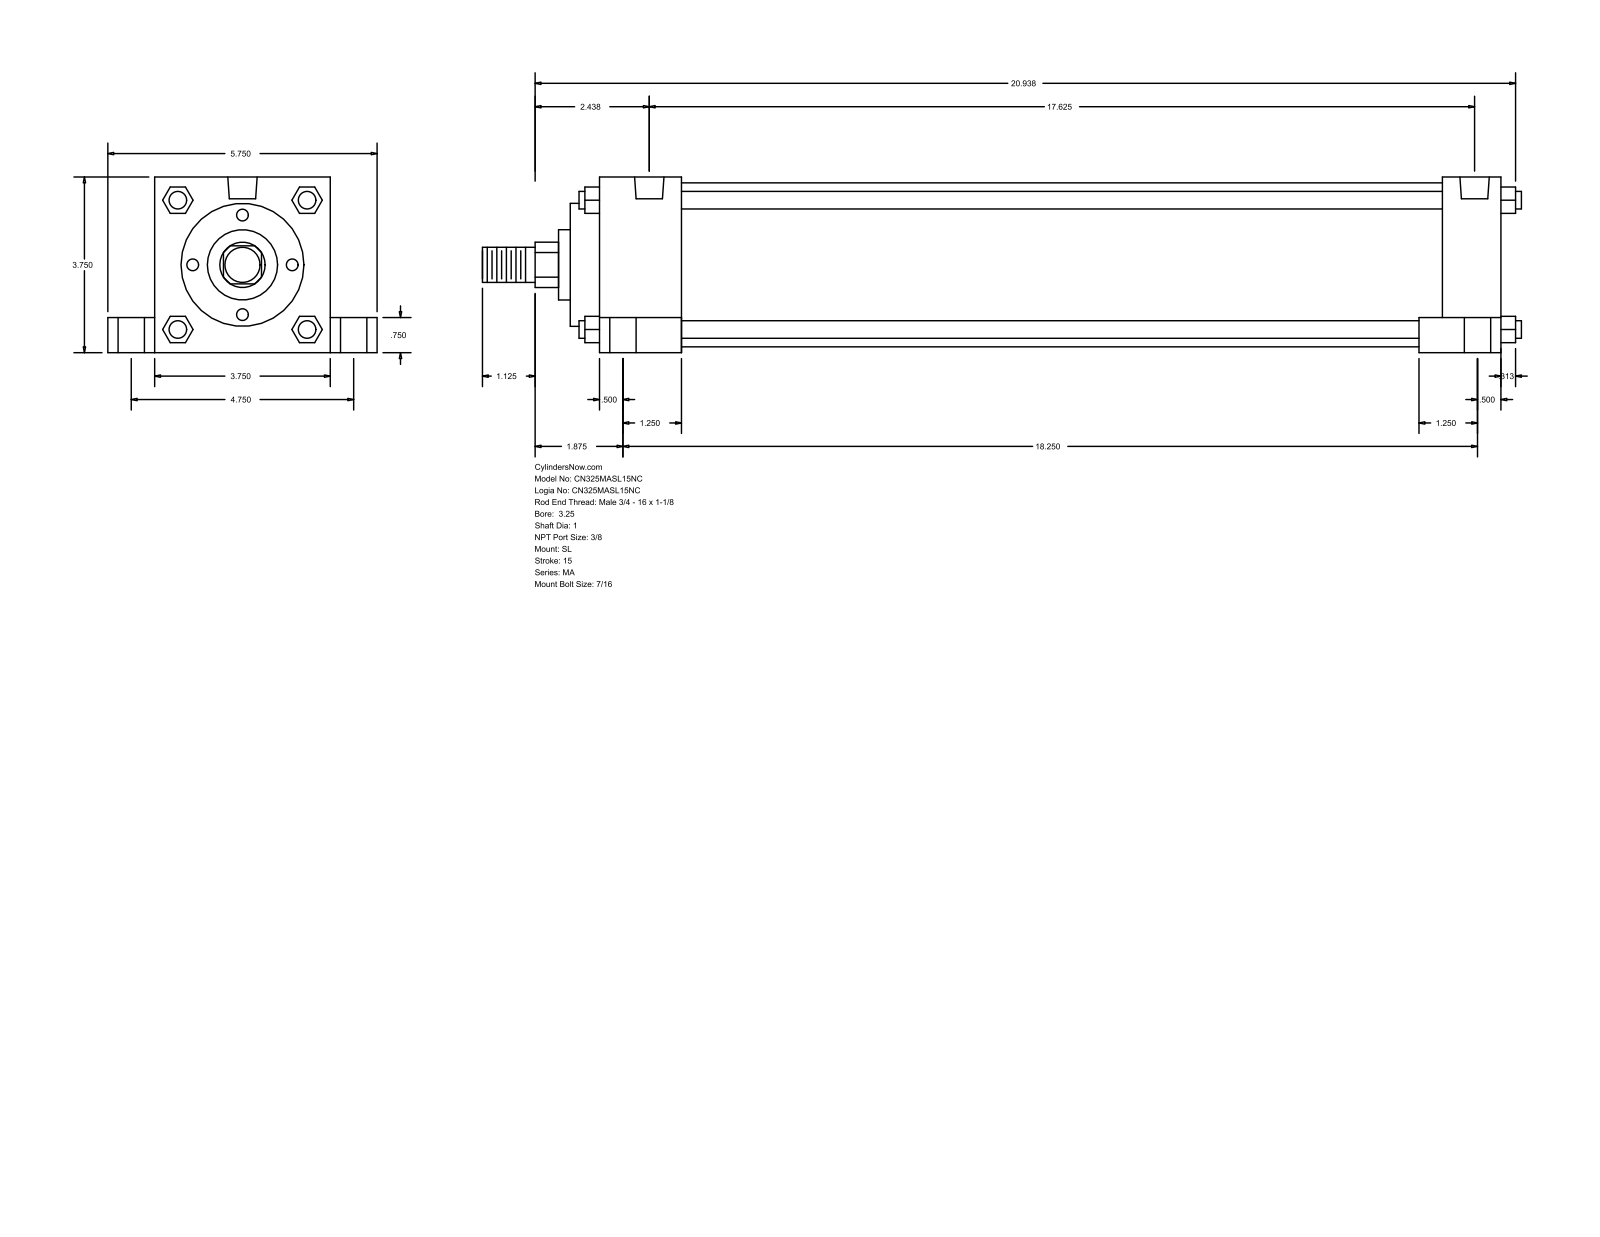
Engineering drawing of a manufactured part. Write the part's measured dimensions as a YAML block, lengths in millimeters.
part_name: "MA_SL__0325_1"
step_written_by: "GSSL Pune (CONFIG_CONTROL_DESIGN)"
units: millimeters
bodies: {solids: 0, faces: 150, planar: 113, cylindrical: 37, other: 0}
overall_size: [563.56, 146.05, 95.25]
round_holes:
  - {diameter: 11.11, count: 4}
  - {diameter: 14.29, count: 4}
  - {diameter: 20.64, count: 4}
  - {diameter: 15.93, count: 2}
round_bosses_or_shafts:
  - {diameter: 9.53, count: 4}
  - {diameter: 88.9, count: 1}
  - {diameter: 66.67, count: 1}
  - {diameter: 38.1, count: 1}
  - {diameter: 25.4, count: 1}
  - {diameter: 19.05, count: 1}
partial_cylinders:
  - {radius: 12.29, count: 1}
face_to_face_distances: [95.24, 488.96, 15.87, 25.41, 120.65, 19.05, 457.2, 31.76, 44.46, 412.74]
hole_center_spacings: [60.35, 60.66, 62, 63.27, 120.66, 438.15, 448.59, 453.3]
